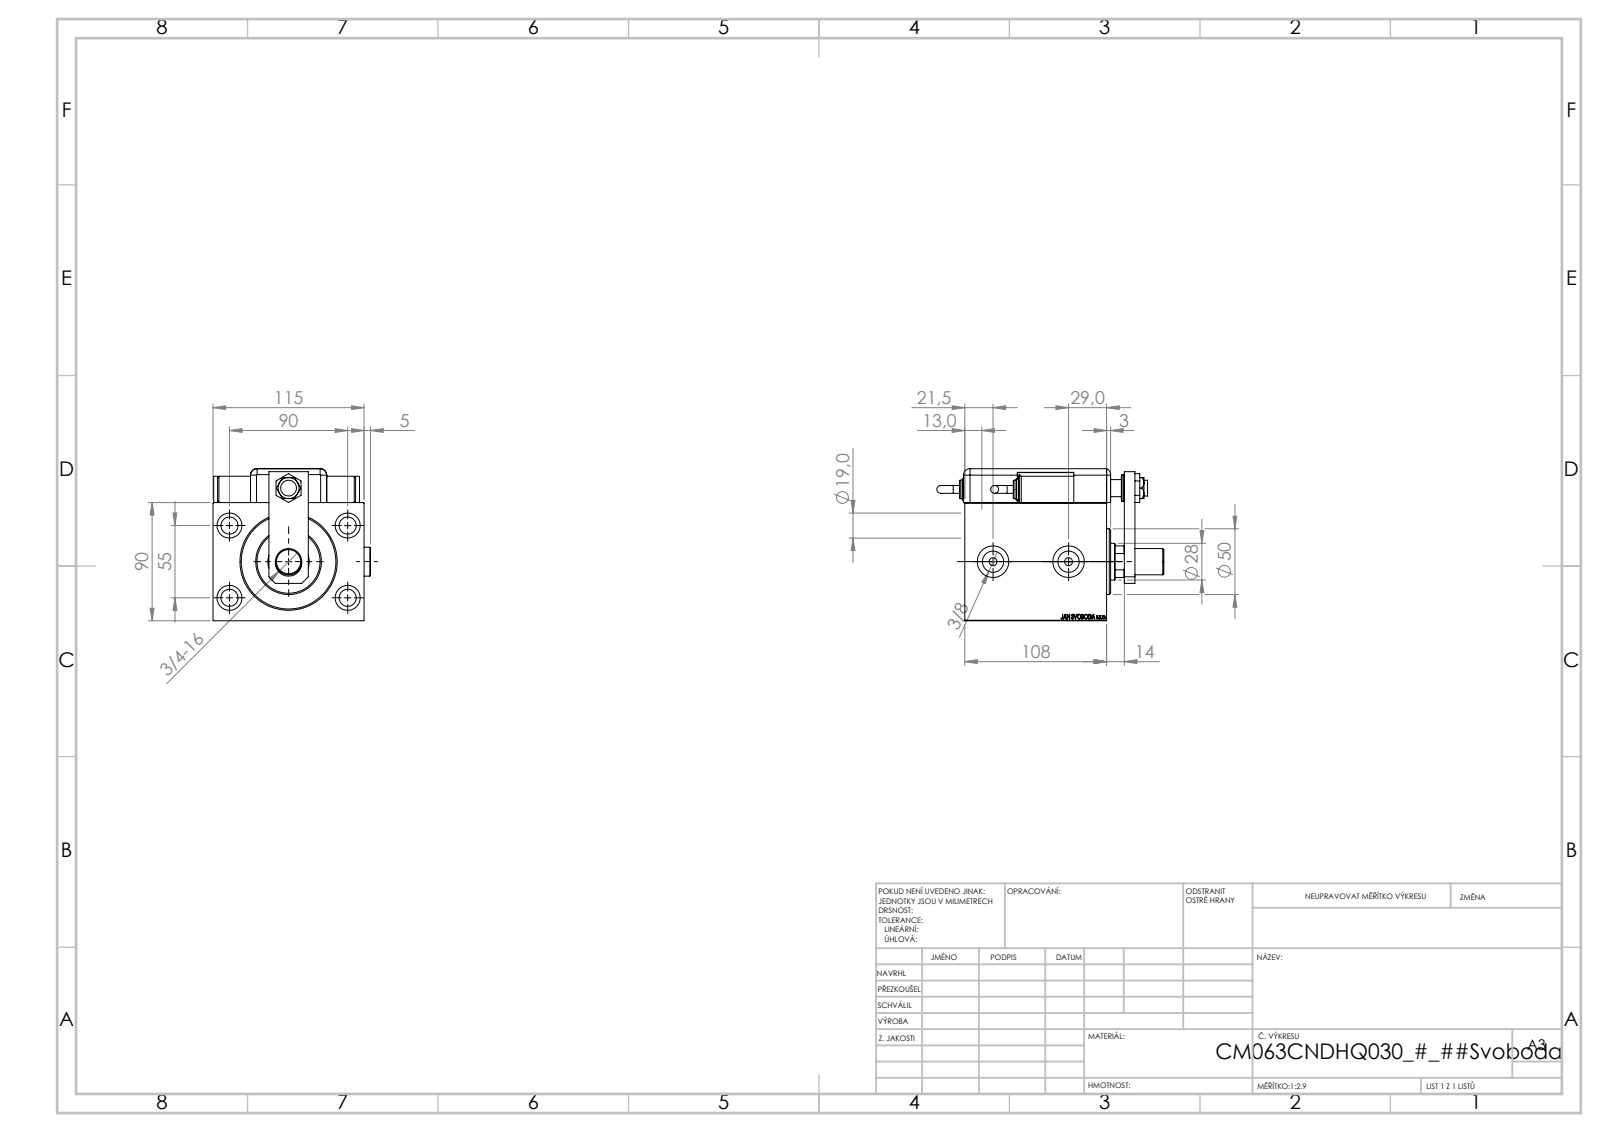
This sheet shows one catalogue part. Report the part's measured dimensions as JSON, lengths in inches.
{"part_name": "V450CM_MALE_METRIC; MAGNETIC SWITCH Q; SWITCH_Q_FRONT_BACK; V450CM_VC_B (+7 more)", "step_written_by": "SolidWorks 2019 (CONFIG_CONTROL_DESIGN)", "units": "inches", "bodies": {"solids": 16, "faces": 1317, "planar": 653, "cylindrical": 137, "other": 527}, "overall_size": [6.802, 4.72, 4.559], "volume_in3": 68.47, "surface_area_in2": 311.5, "round_holes": [[0.512, 5], [0.748, 4], [0.157, 2], [0.236, 2], [0.315, 2], [0.637, 2], [0.945, 2], [0.472, 1], [0.551, 1], [0.728, 1], [0.787, 1], [1.102, 1]], "round_bosses_or_shafts": [[0.787, 4], [0.866, 2], [0.63, 2], [0.551, 2], [0.236, 2], [1.969, 1], [0.709, 1]], "partial_cylinders_radius": [[0.197, 9], [0.394, 1], [0.531, 1]], "face_to_face_distances": [3.543, 0.118, 4.252, 4.528, 3.563, 0.689, 0.531, 0.728, 0.315, 1.016], "hole_center_spacings": [2.076, 2.097, 2.056, 2.165, 3.543, 3.734, 4.153, 0.039]}
